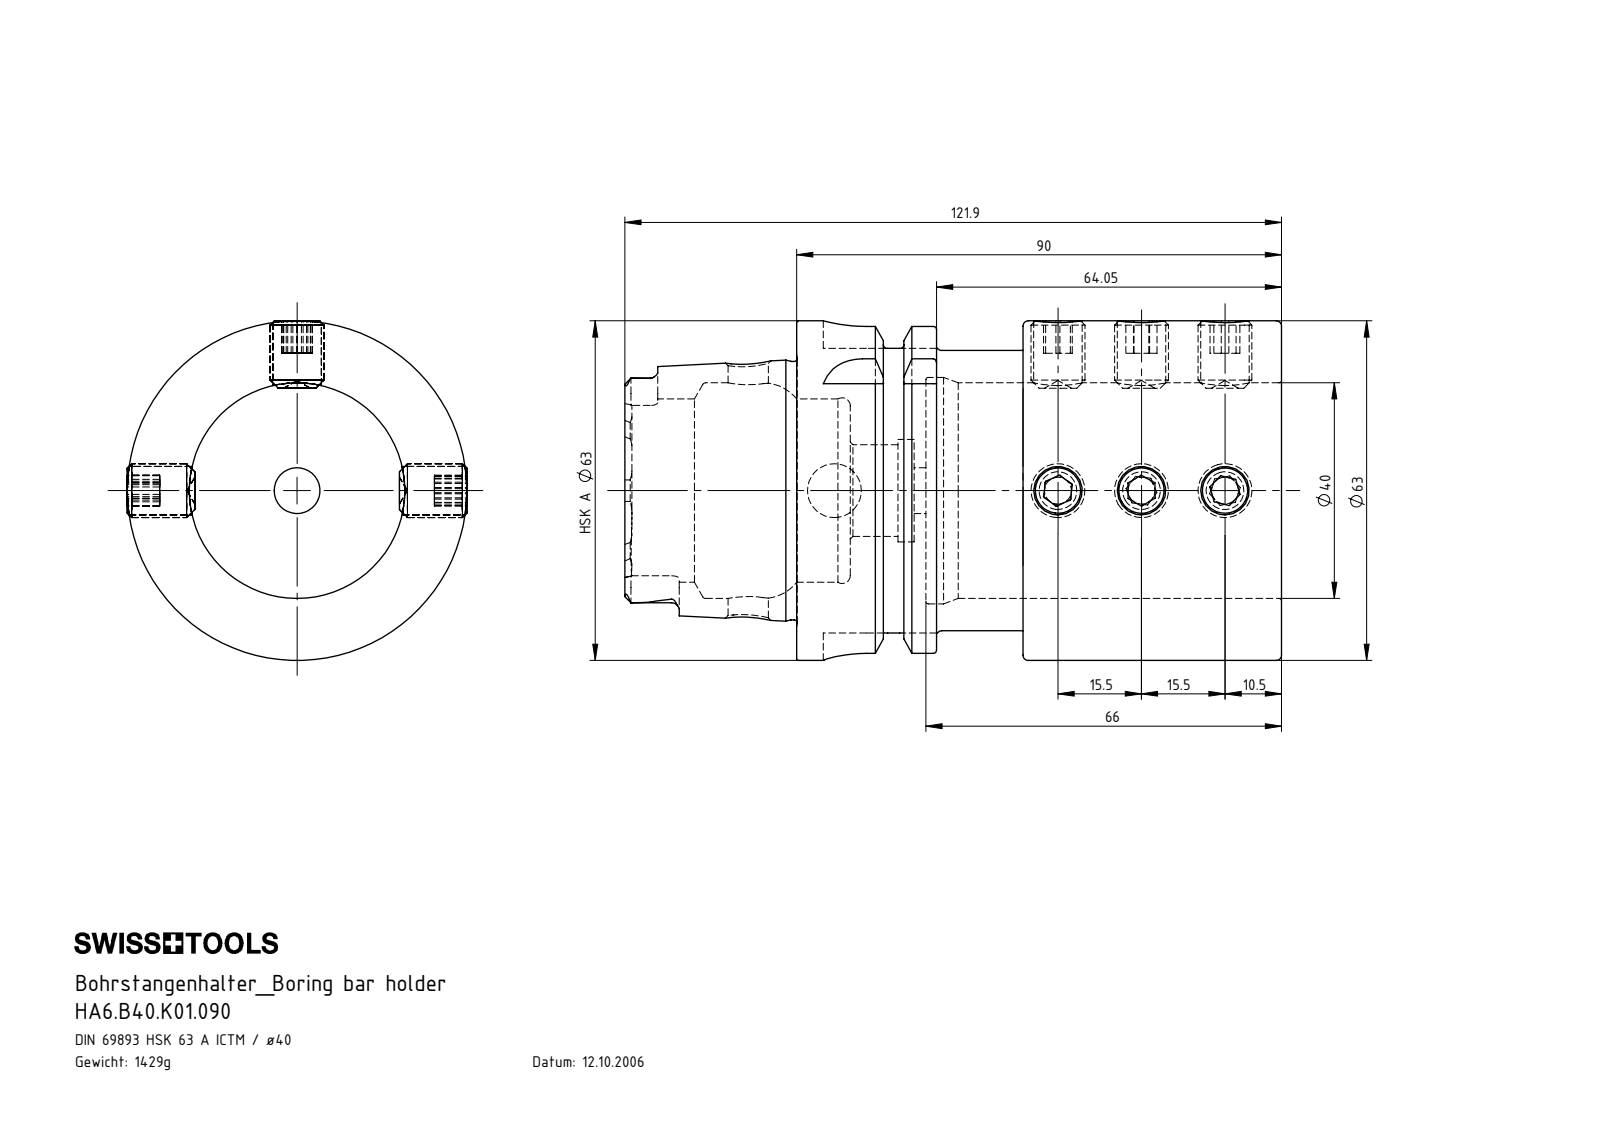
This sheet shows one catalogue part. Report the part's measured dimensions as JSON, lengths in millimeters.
{"part_name": "ISO 4026 - M10 x 12_PreviewCfg; HA6.B40.K01.090; HA6-B40.K01.090_B_Fertigbearbeitung", "step_written_by": "SolidWorks 2017 (AUTOMOTIVE_DESIGN)", "units": "millimeters", "bodies": {"solids": 11, "faces": 369, "planar": 139, "cylindrical": 89, "other": 141}, "overall_size": [121.9, 63, 63], "volume_mm3": 182517, "surface_area_mm2": 52124, "round_holes": [[9, 6], [7.5, 1], [8.5, 1], [10, 1], [17, 1], [19, 1], [34, 1], [40, 1], [42, 1]], "round_bosses_or_shafts": [[10, 6], [63, 1], [54.95, 1], [52, 1], [47.94, 1]], "partial_cylinders_radius": [[1.4, 6], [2.88, 4], [8, 4]], "face_to_face_distances": [66, 24, 90, 18, 42, 48, 25.95, 1.95, 16.05, 64.05], "hole_center_spacings": [15.5, 31, 41.5, 57, 57.5, 72.5, 73, 88.5]}
